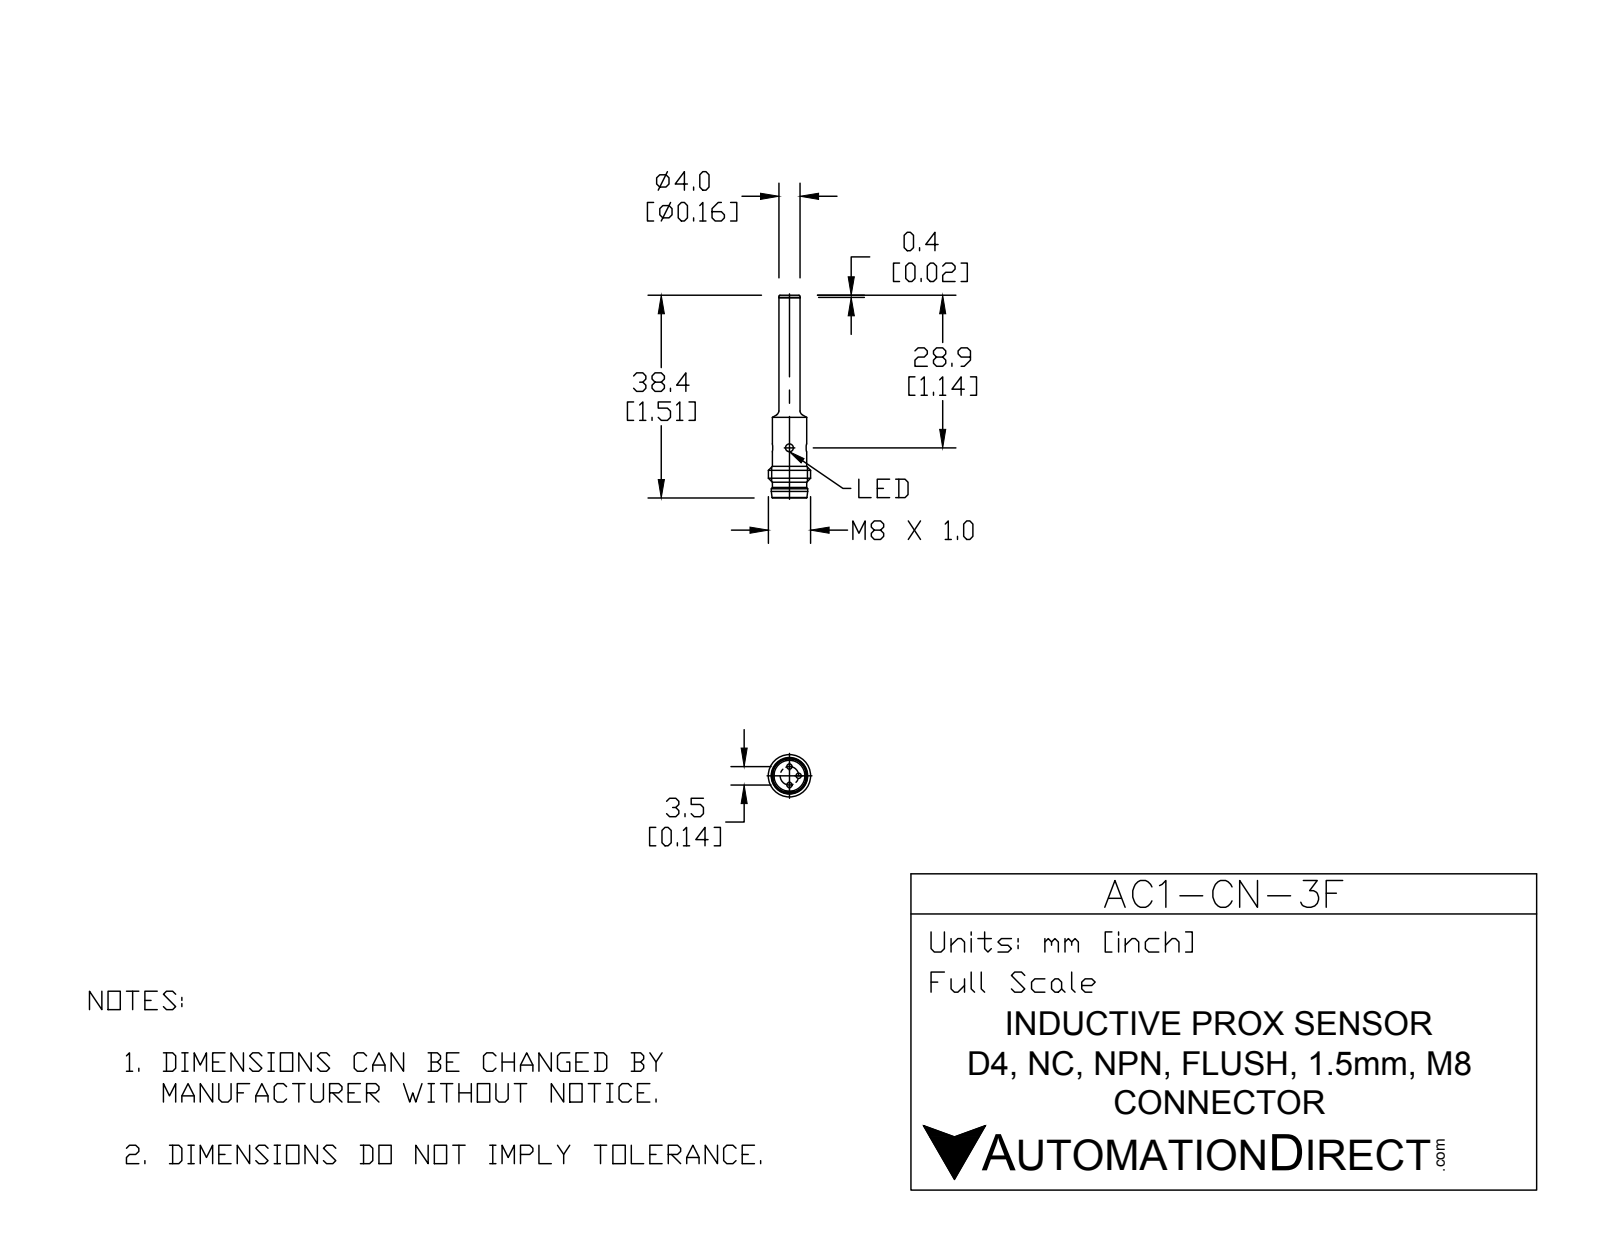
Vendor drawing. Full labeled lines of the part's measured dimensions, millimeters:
Part name (STEP PRODUCT): AC1-CN-3F
STEP written by: SolidWorks 2015 (CONFIG_CONTROL_DESIGN)
Units: millimetres
Bodies: 4 solids, 59 faces (11 planar, 26 cylindrical, 22 other)
Overall size (bounding box): 38.4 × 8 × 8
Volume: 757 mm³ · Surface area: 840 mm²
Round holes (diameter × count): ⌀1.5 ×2, ⌀5.85 ×1
Round bosses / shafts (diameter × count): ⌀1 ×3, ⌀8 ×1, ⌀6.9 ×1, ⌀6.5 ×1, ⌀4 ×1
Main face-to-face distances: 33.4, 5.5, 5, 38.4, 38, 33, 0.4
